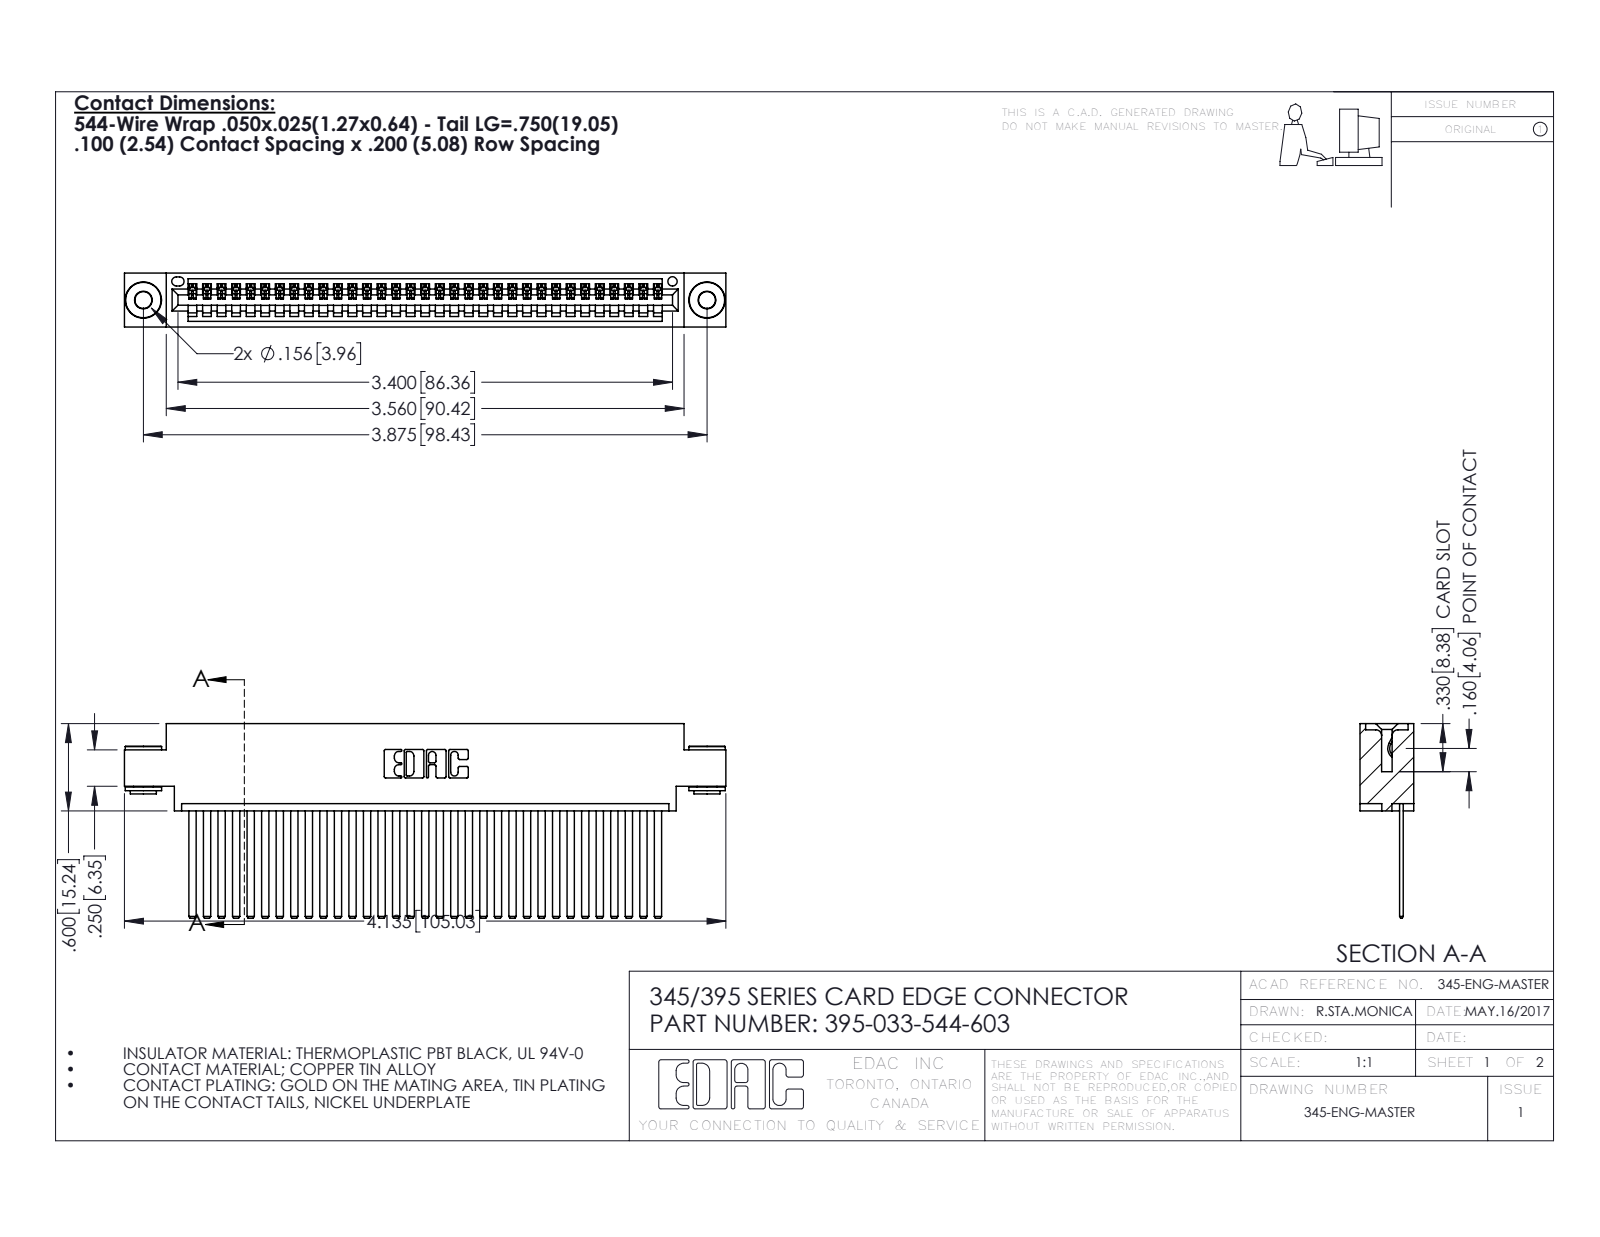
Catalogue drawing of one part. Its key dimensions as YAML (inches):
part_name: "345-292-001_345-293-144; 345-250-002_345-250-002-102; 345 Part_0.170 Offset - 0.156 Dia-TH; 395-033-544-603"
step_written_by: "SolidWorks 2016 (CONFIG_CONTROL_DESIGN)"
units: inches
bodies: {solids: 36, faces: 1884, planar: 1282, cylindrical: 594, other: 8}
overall_size: [4.135, 1.337, 0.37]
volume: 0.622
surface_area: 23.11
round_holes:
  - {diameter: 0.116, count: 2}
  - {diameter: 0.156, count: 2}
  - {diameter: 0.064, count: 1}
round_bosses_or_shafts:
  - {diameter: 0.25, count: 2}
  - {diameter: 0.18, count: 2}
  - {diameter: 0.136, count: 2}
partial_cylinders:
  - {radius: 0.006, count: 66}
  - {radius: 0.01, count: 22}
  - {radius: 0.007, count: 6}
  - {radius: 0.031, count: 6}
  - {radius: 0.026, count: 3}
  - {radius: 0.031, count: 2}
  - {radius: 0.04, count: 2}
  - {radius: 0.014, count: 1}
face_to_face_distances: [0.072, 0.298, 0.025, 0.098, 0.272, 0.37, 0.2, 0.225, 0.175, 0.149]
hole_center_spacings: [0.27, 3.64, 3.875]
